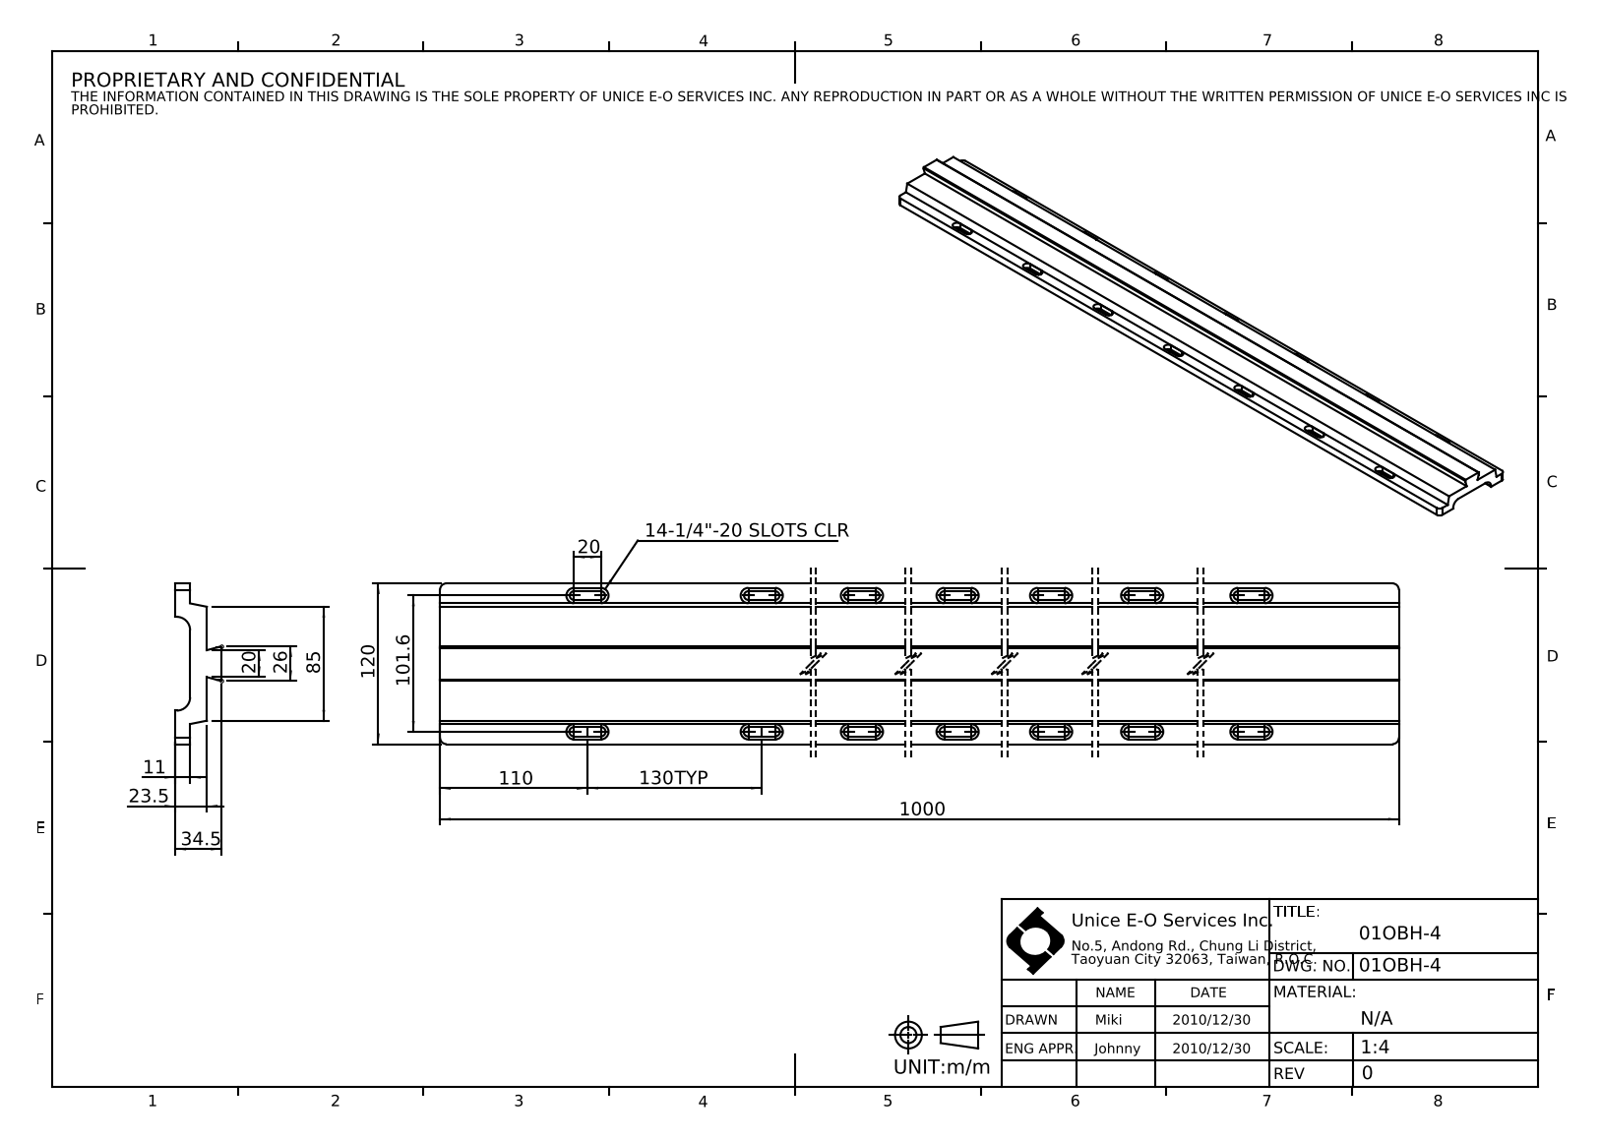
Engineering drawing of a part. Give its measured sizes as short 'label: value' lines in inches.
name: 01OBH-4
written by: SolidWorks 2016 (CONFIG_CONTROL_DESIGN)
unit: in
bodies: 0 solids, 189 faces (88 planar, 101 cylindrical, 0 other)
size: 39.37 × 4.724 × 1.358
holes: 2× ⌀0.197
rounds: 28× R0.226, 14× R0.128, 14× R0.138, 6× R0.039, 4× R0.197, 2× R0.394
face distances: 0.433, 0.925, 0.492, 1.358, 4.724, 0.276, 0.157, 0.768, 1.201, 0.984
hole spacings: 38.189
